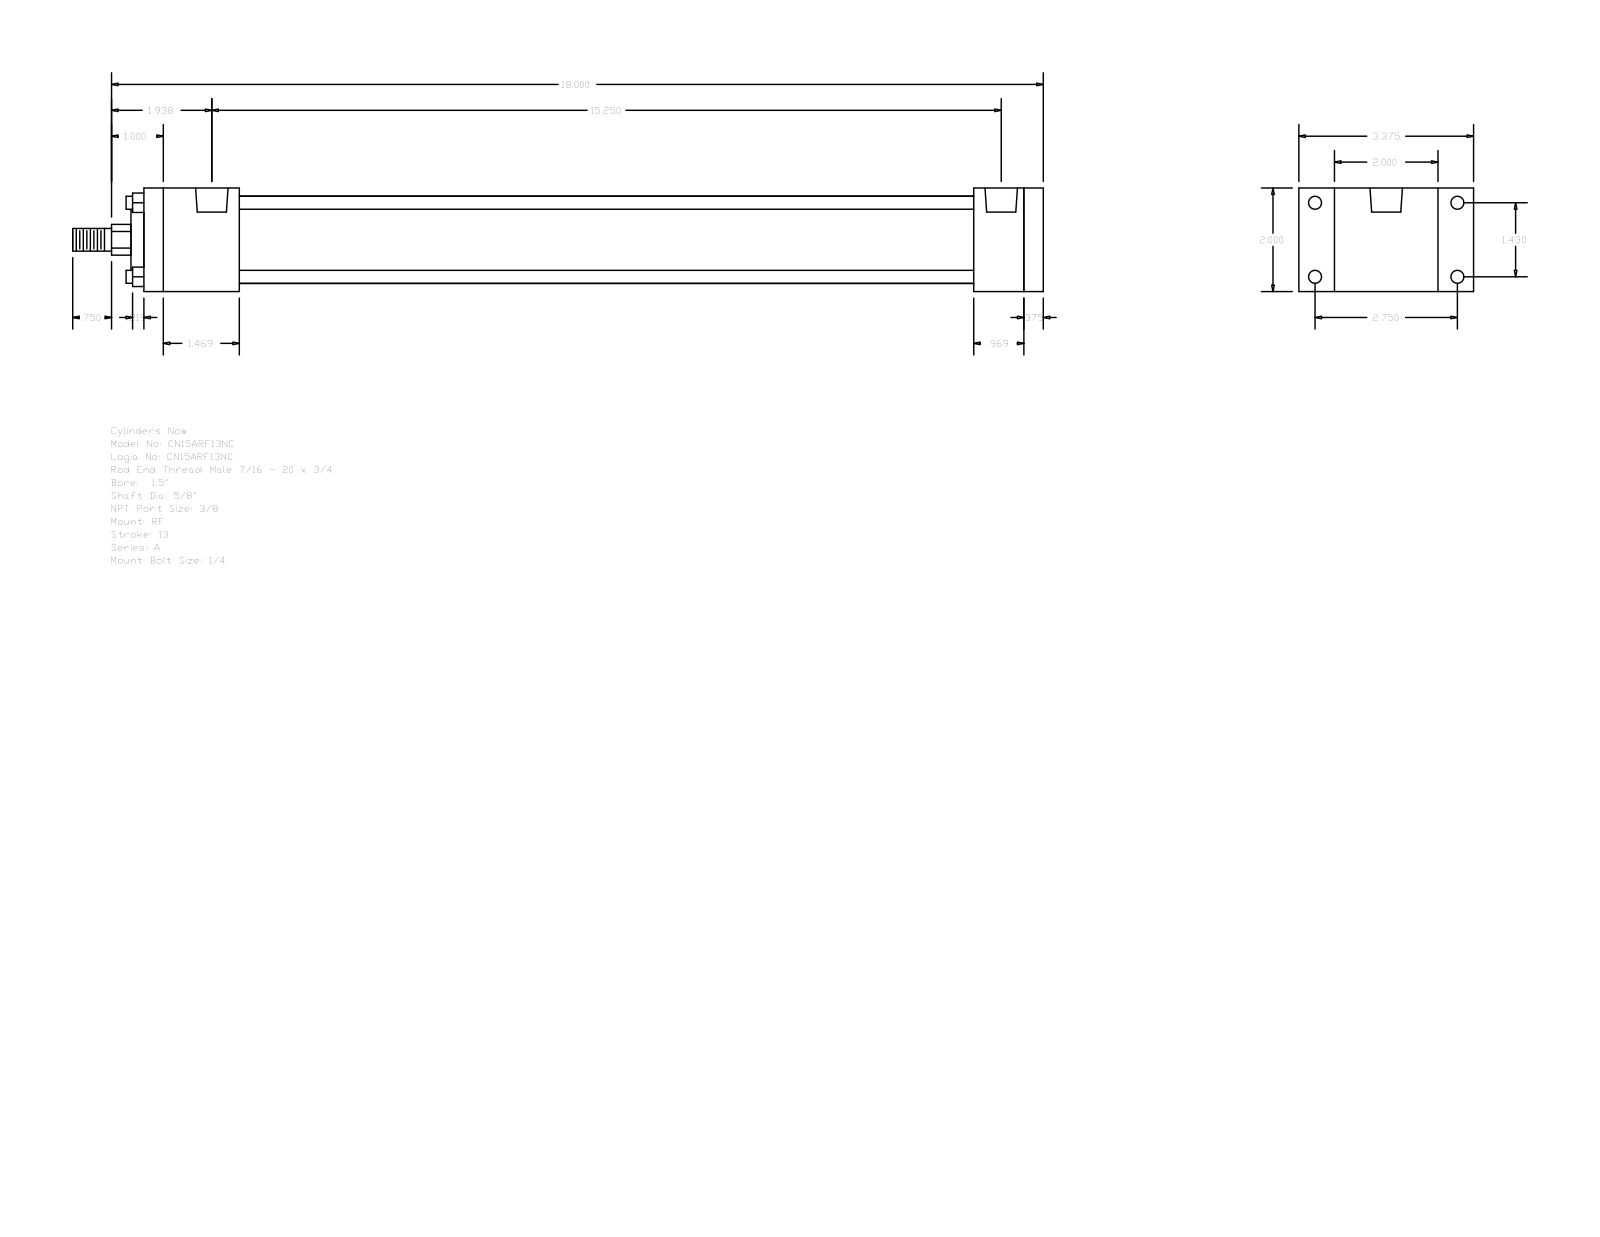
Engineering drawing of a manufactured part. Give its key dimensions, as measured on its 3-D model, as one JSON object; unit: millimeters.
{"part_name": "A_RF__0150_0.625", "step_written_by": "GSSL Pune (CONFIG_CONTROL_DESIGN)", "units": "millimeters", "bodies": {"solids": 0, "faces": 92, "planar": 64, "cylindrical": 28, "other": 0}, "overall_size": [476.25, 85.72, 50.8], "round_holes": [[5.56, 4], [6.35, 4], [15.93, 2]], "round_bosses_or_shafts": [[6.35, 4], [42.93, 1], [28.57, 1], [15.88, 1], [11.11, 1]], "partial_cylinders_radius": [[7.54, 1]], "face_to_face_distances": [50.8, 9.52, 431.8, 441.32, 407.19, 24.61, 34.13, 46.83, 360.36, 384.97], "hole_center_spacings": [3.97, 36.32, 69.84, 78.72, 379.41, 383.38, 387.35]}
